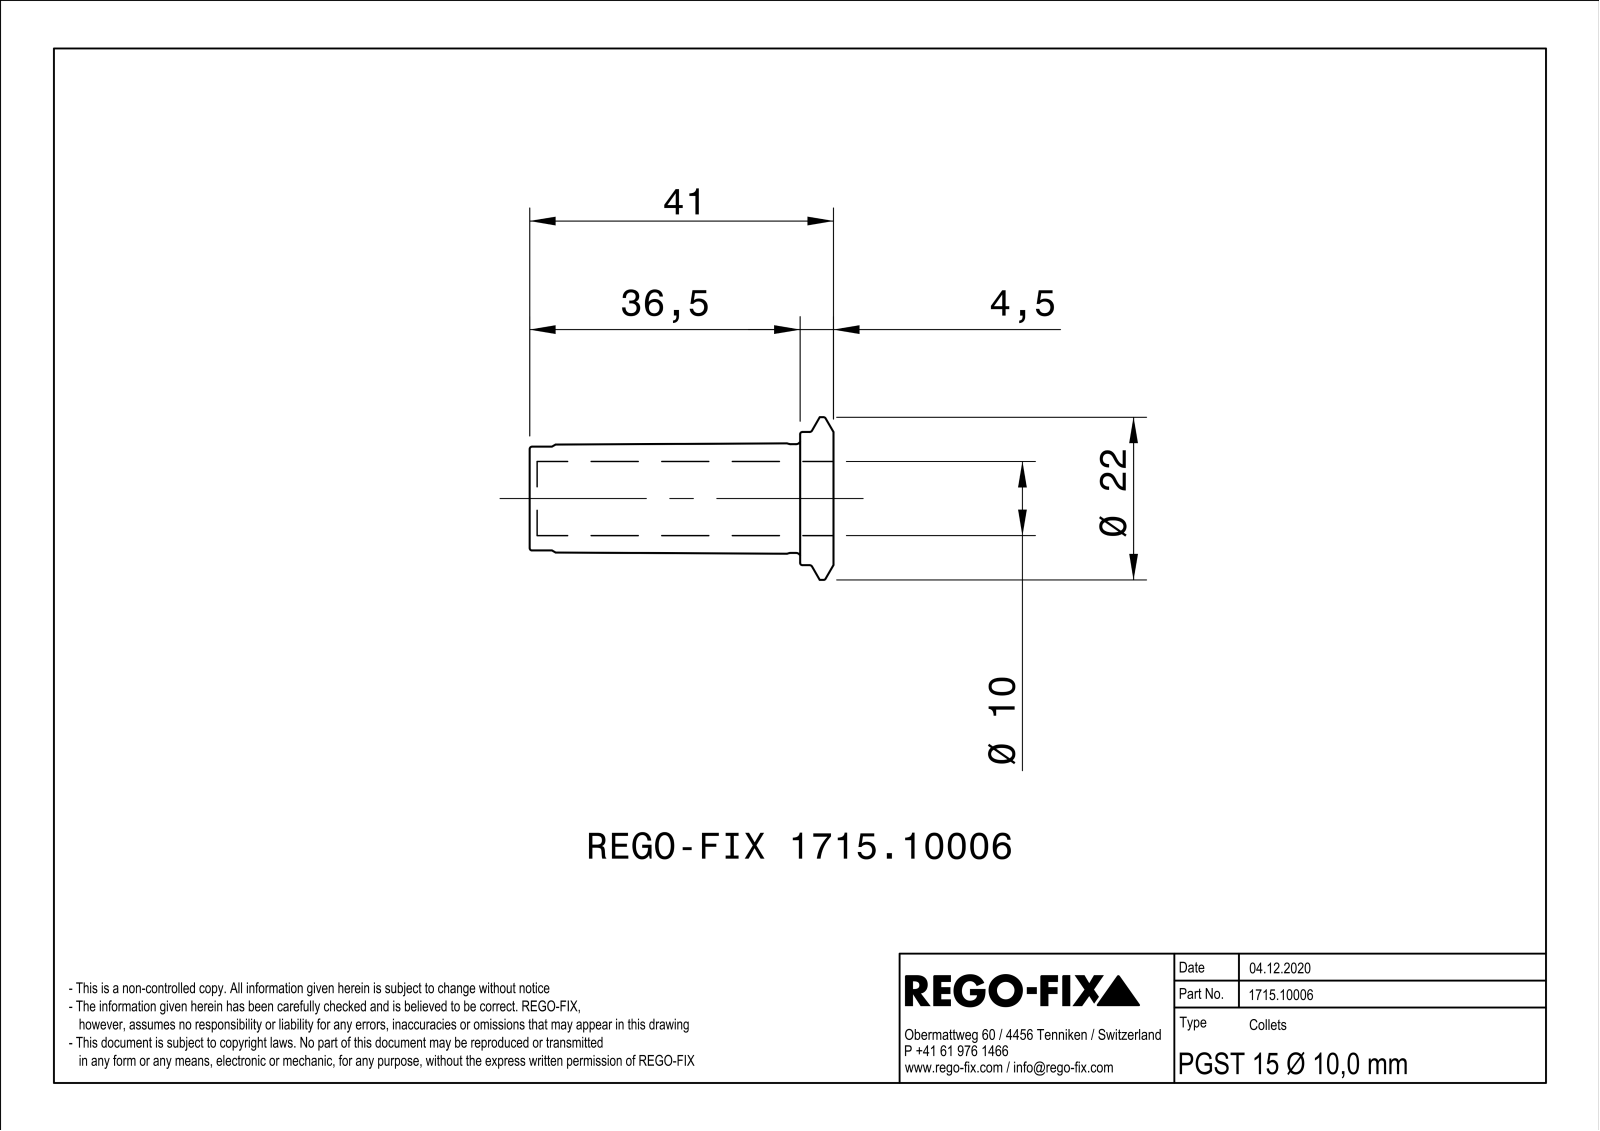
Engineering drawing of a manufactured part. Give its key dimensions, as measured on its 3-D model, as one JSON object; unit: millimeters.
{"part_name": "NOCUT", "step_written_by": "SIEMENS PLM Software Solid Edge ST10 (AUTOMOTIVE_DESIGN)", "units": "millimeters", "bodies": {"solids": 2, "faces": 42, "planar": 7, "cylindrical": 14, "other": 21}, "overall_size": [41, 21.98, 21.98], "volume_mm3": 4383, "surface_area_mm2": 4196, "round_holes": [[1.5, 3], [5, 1], [10, 1], [10.2, 1], [11.46, 1], [12.5, 1]], "round_bosses_or_shafts": [[21.98, 1], [18, 1], [14.7, 1], [14, 1], [12, 1], [11.1, 1]], "face_to_face_distances": [41, 4.5, 36.5, 40, 1, 3.5, 32, 35.5], "hole_center_spacings": [4, 6.93, 6.92]}
